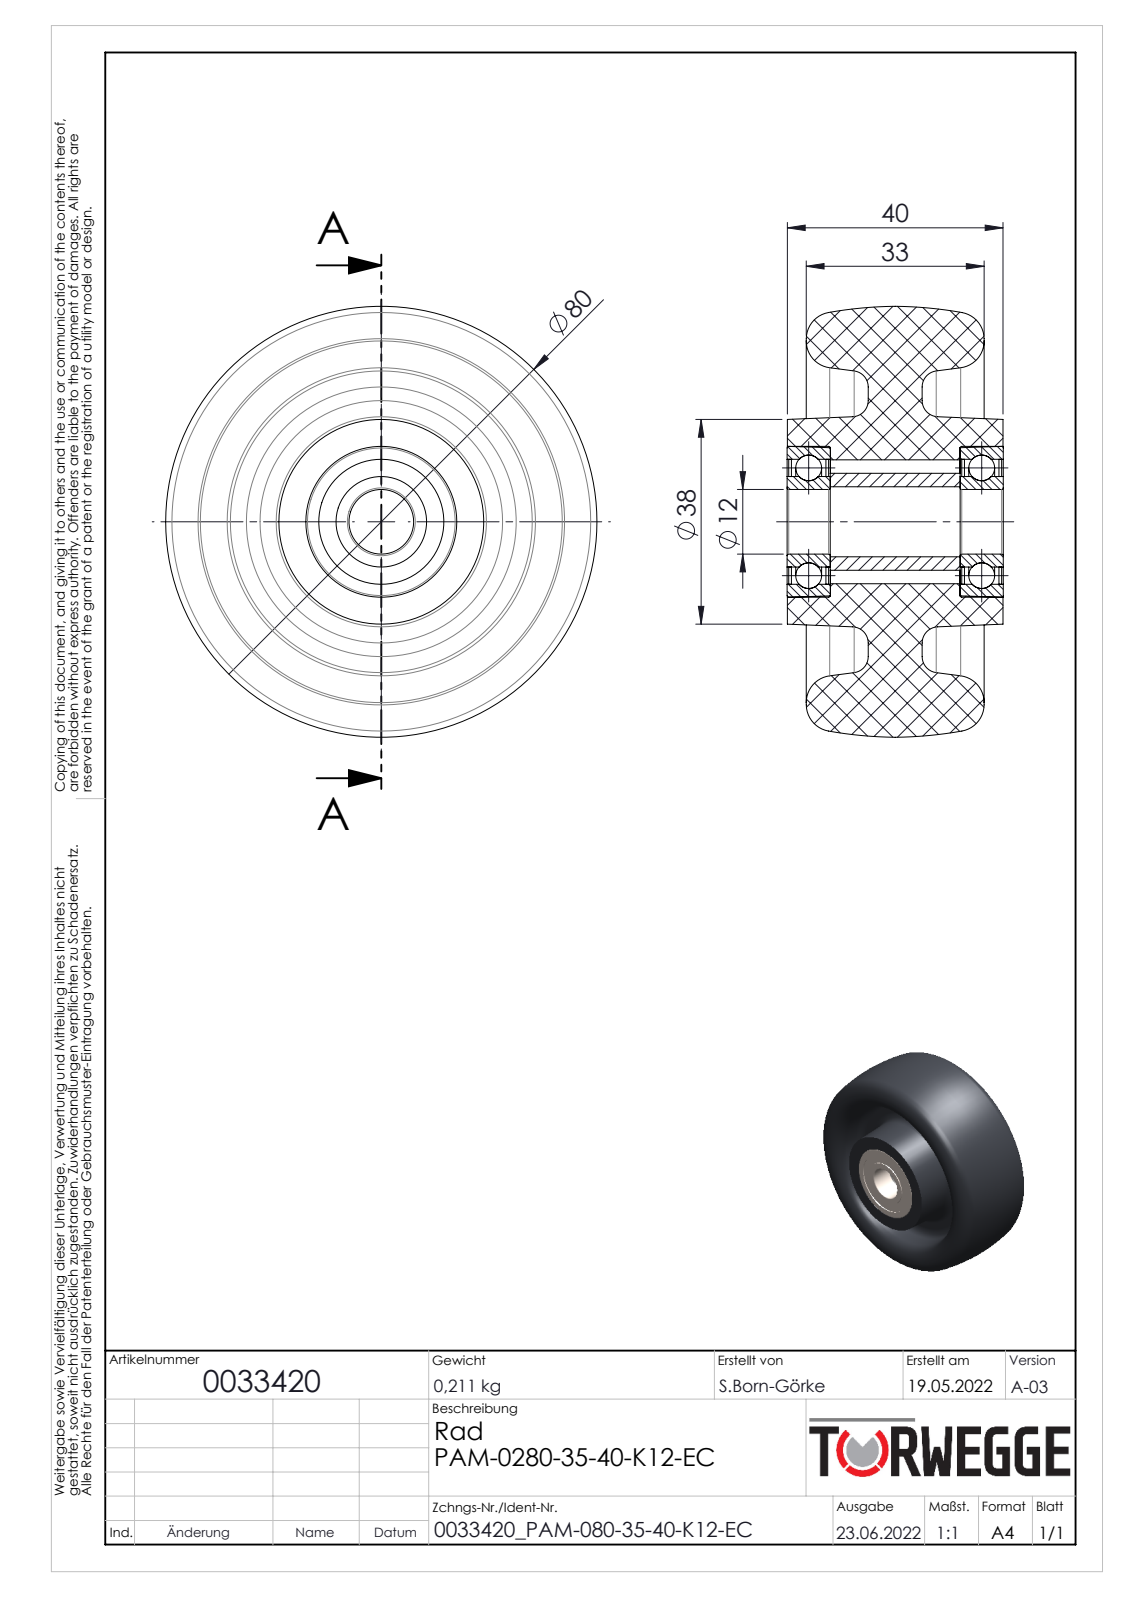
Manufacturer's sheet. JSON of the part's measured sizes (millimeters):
{"part_name": "0033420", "step_written_by": "SolidWorks 2020 (AUTOMOTIVE_DESIGN)", "units": "millimeters", "bodies": {"solids": 12, "faces": 142, "planar": 24, "cylindrical": 46, "other": 72}, "overall_size": [80, 80, 40.1], "volume_mm3": 125189, "surface_area_mm2": 36449, "round_holes": [[12, 1], [13, 1], [16.8, 1], [23, 1], [23.2, 1]], "round_bosses_or_shafts": [[28, 1], [18, 1]], "face_to_face_distances": [32.1, 32.05, 8, 0.8, 7.2, 7.7, 0.5, 6.9, 7.95, 15]}
